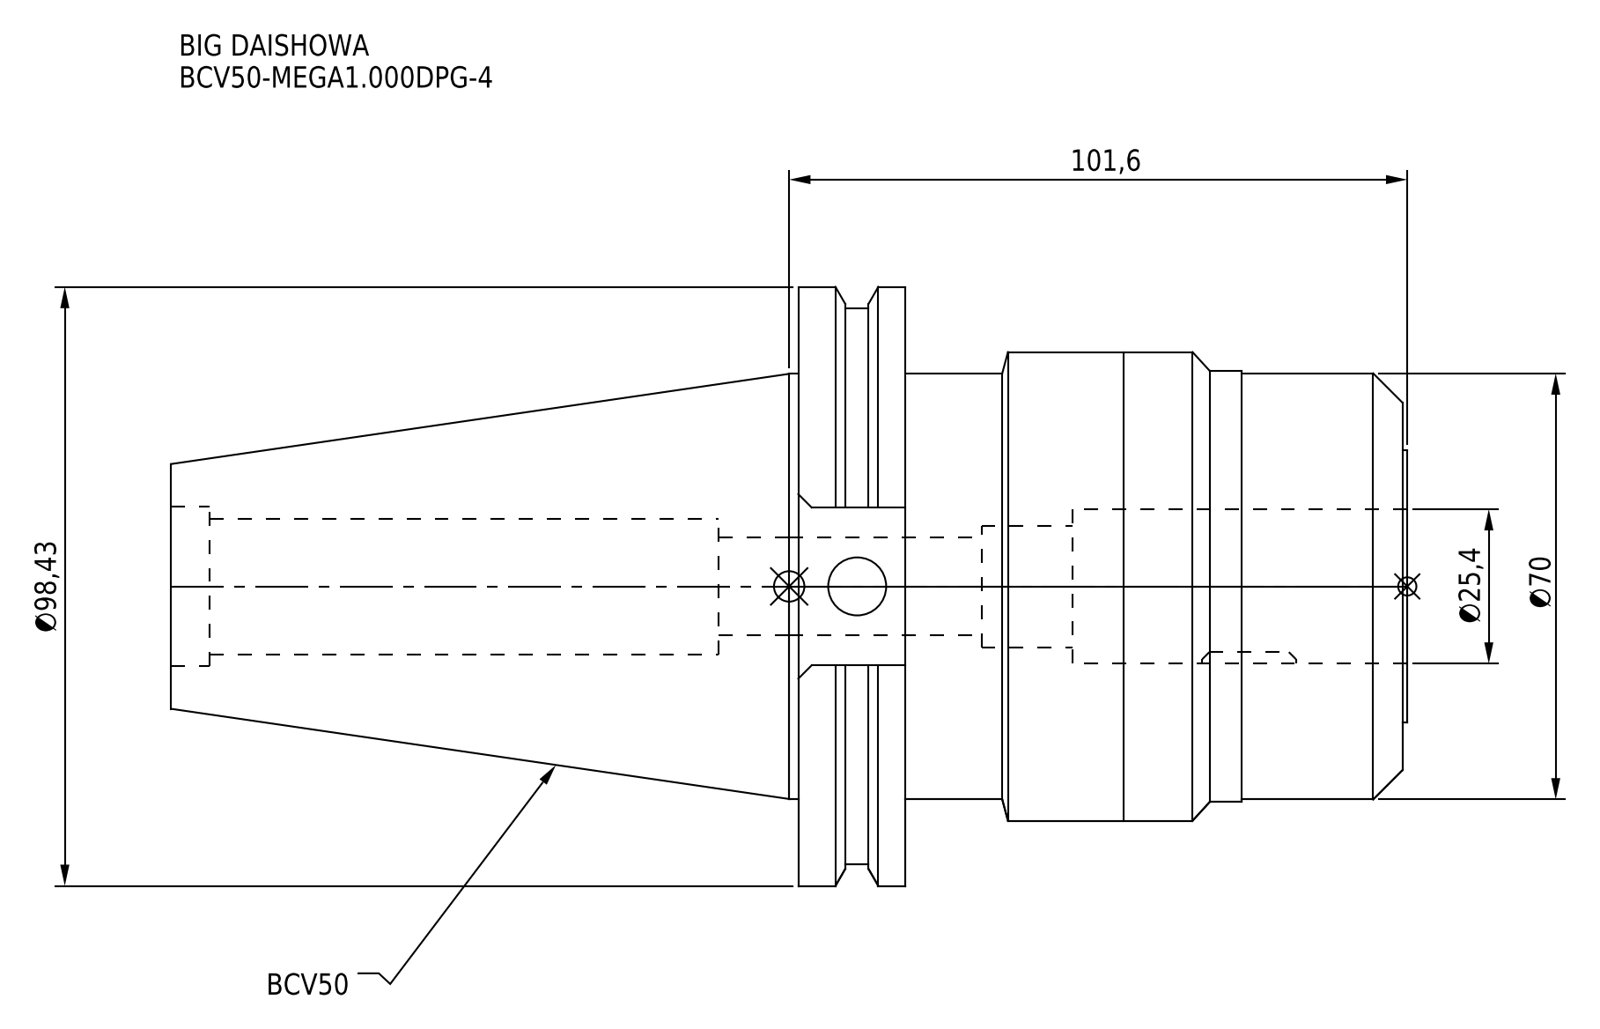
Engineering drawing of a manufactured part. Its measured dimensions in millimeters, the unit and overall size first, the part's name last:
Units: millimetres
Overall size (bounding box): 203.2 × 98.42 × 94.95
Round holes (diameter × count): ⌀9.53 ×1, ⌀16 ×1, ⌀20 ×1, ⌀22.3 ×1, ⌀25.4 ×1, ⌀26.23 ×1
Round bosses / shafts (diameter × count): ⌀98.42 ×1, ⌀91.29 ×1, ⌀77 ×1, ⌀70.7 ×1, ⌀70 ×1, ⌀69.85 ×1, ⌀44.8 ×1
Main face-to-face distances: 17.55, 81.75, 99.3, 0.8, 82.55, 100.1, 203.2, 202.4, 120.65, 103.1
Volume: 633 489 mm³ · Surface area: 69 286 mm²
Bodies: 1 solid, 69 faces (25 planar, 32 cylindrical, 12 other)
Part name (STEP PRODUCT): BCV50-MEGA1_000DPG-4
STEP written by: CREO PARAMETRIC BY PTC INC, 2016380 (AUTOMOTIVE_DESIGN)
